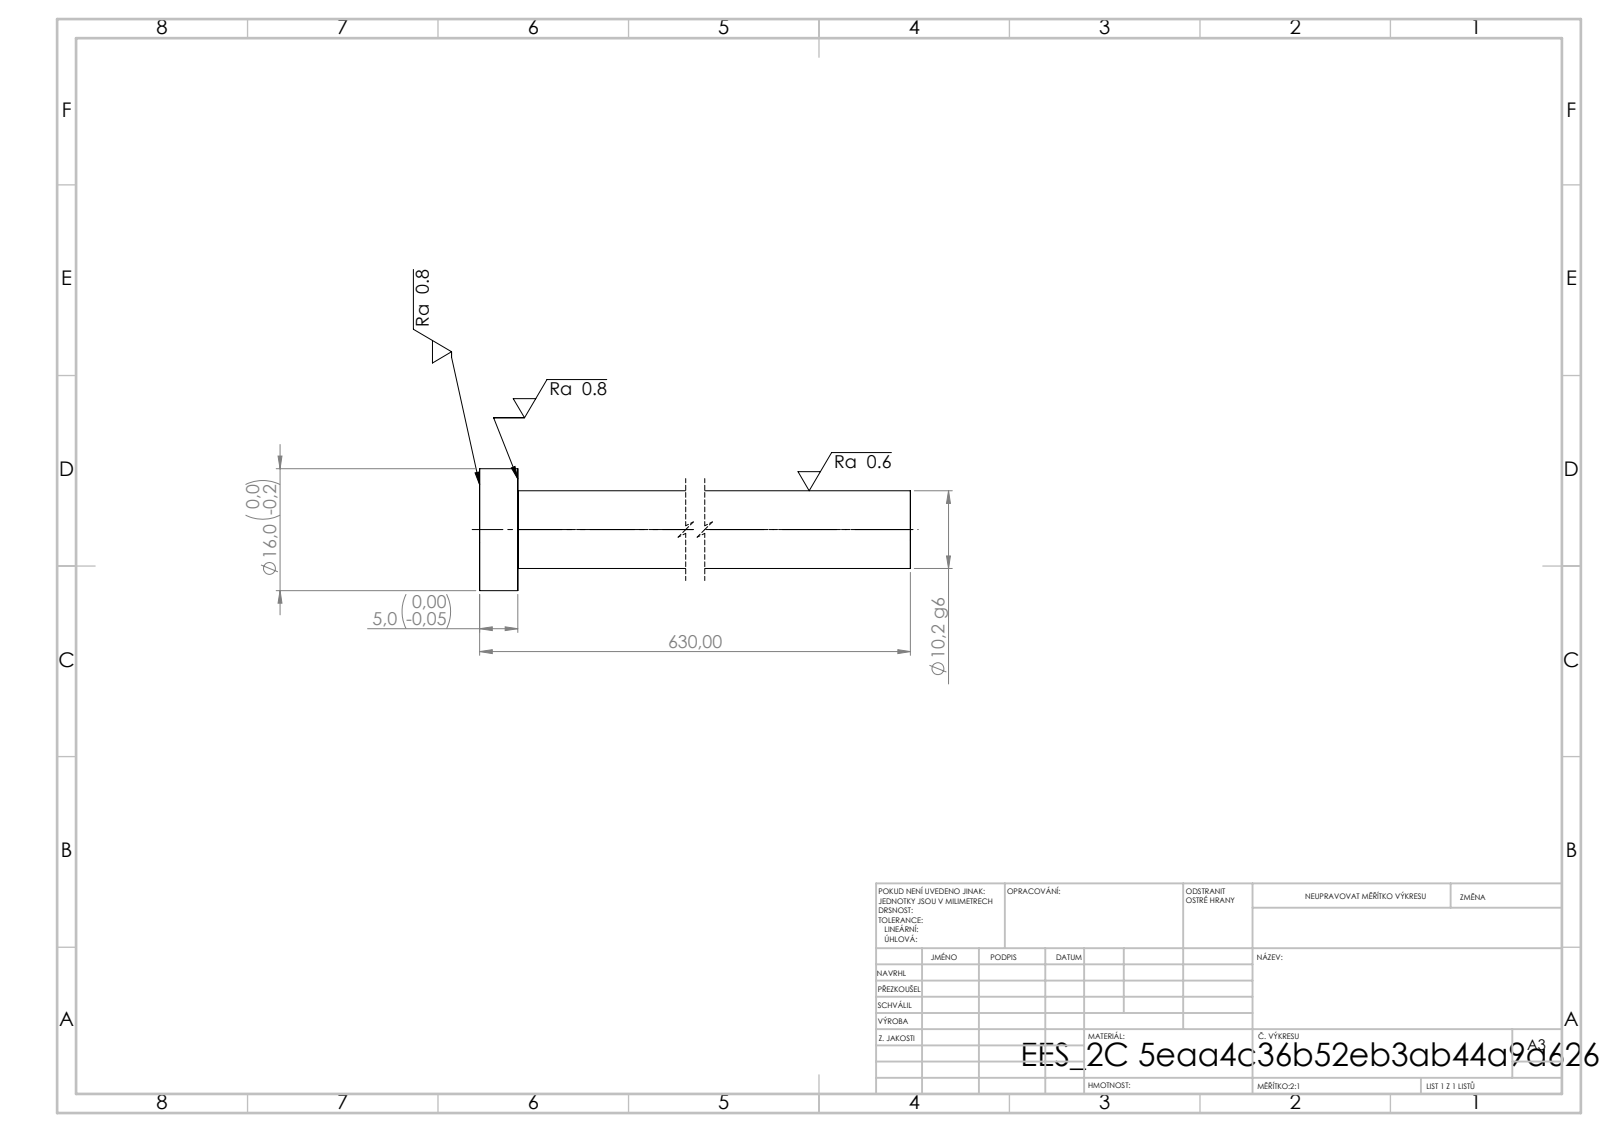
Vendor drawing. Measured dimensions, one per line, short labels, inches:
written by: SolidWorks 2019 (CONFIG_CONTROL_DESIGN)
unit: in
bodies: 1 solid, 7 faces (3 planar, 4 cylindrical, 0 other)
size: 24.803 × 0.63 × 0.63
volume: 3.178 in³; area: 32.06 in²
bosses: 1× ⌀0.63, 1× ⌀0.402
face distances: 0.197, 24.803, 24.606
